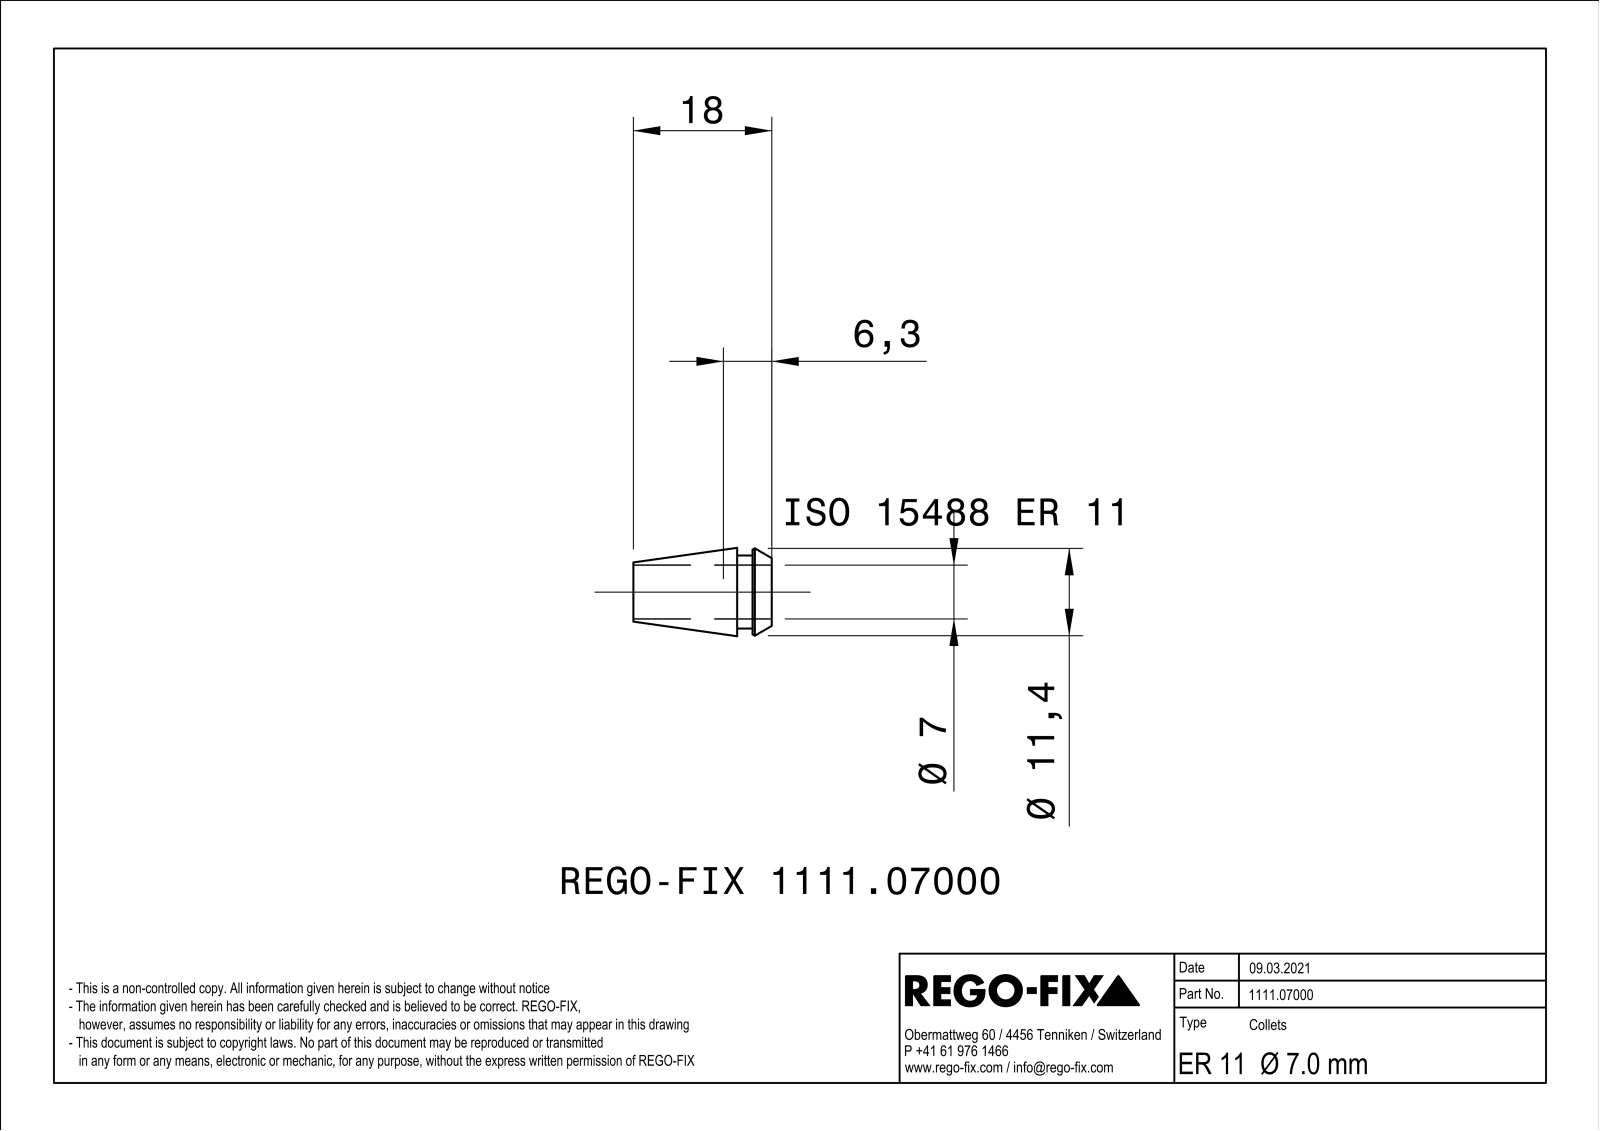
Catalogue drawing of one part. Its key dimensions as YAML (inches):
part_name: "NOCUT"
step_written_by: "SIEMENS PLM Software Solid Edge ST10 (AUTOMOTIVE_DESIGN)"
units: inches
bodies: {solids: 1, faces: 157, planar: 66, cylindrical: 37, other: 54}
overall_size: [0.709, 0.453, 0.452]
volume: 0.033
surface_area: 2.119
round_holes:
  - {diameter: 0.276, count: 1}
round_bosses_or_shafts:
  - {diameter: 0.453, count: 1}
  - {diameter: 0.374, count: 1}
partial_cylinders:
  - {radius: 0.984, count: 12}
face_to_face_distances: [0.018, 0.018, 0.017, 0.079, 0.098, 0.177, 0.157, 0.059, 0.02, 0.551]
